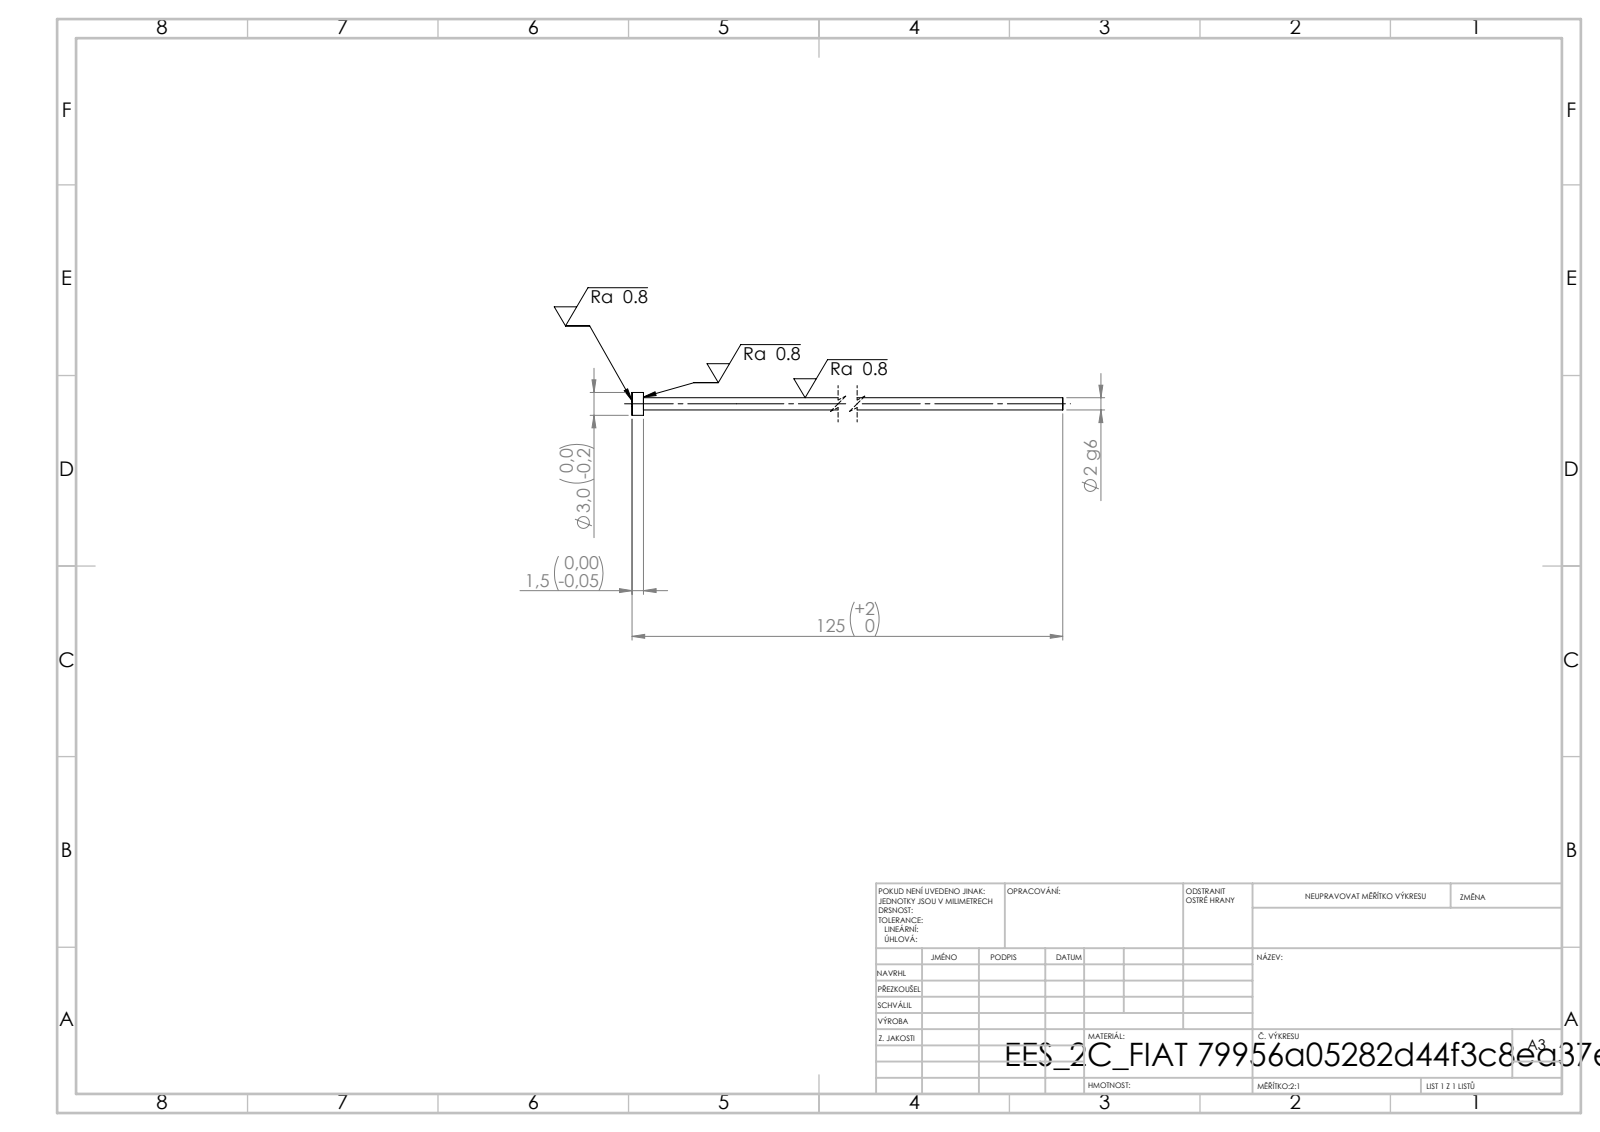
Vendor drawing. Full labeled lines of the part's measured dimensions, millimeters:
STEP written by: SolidWorks 2019 (CONFIG_CONTROL_DESIGN)
Units: millimetres
Bodies: 1 solid, 7 faces (3 planar, 4 cylindrical, 0 other)
Overall size (bounding box): 125 × 3 × 3
Volume: 259 mm³ · Surface area: 649 mm²
Round bosses / shafts (diameter × count): ⌀3 ×1, ⌀1.6 ×1
Main face-to-face distances: 1.5, 125, 123.5
